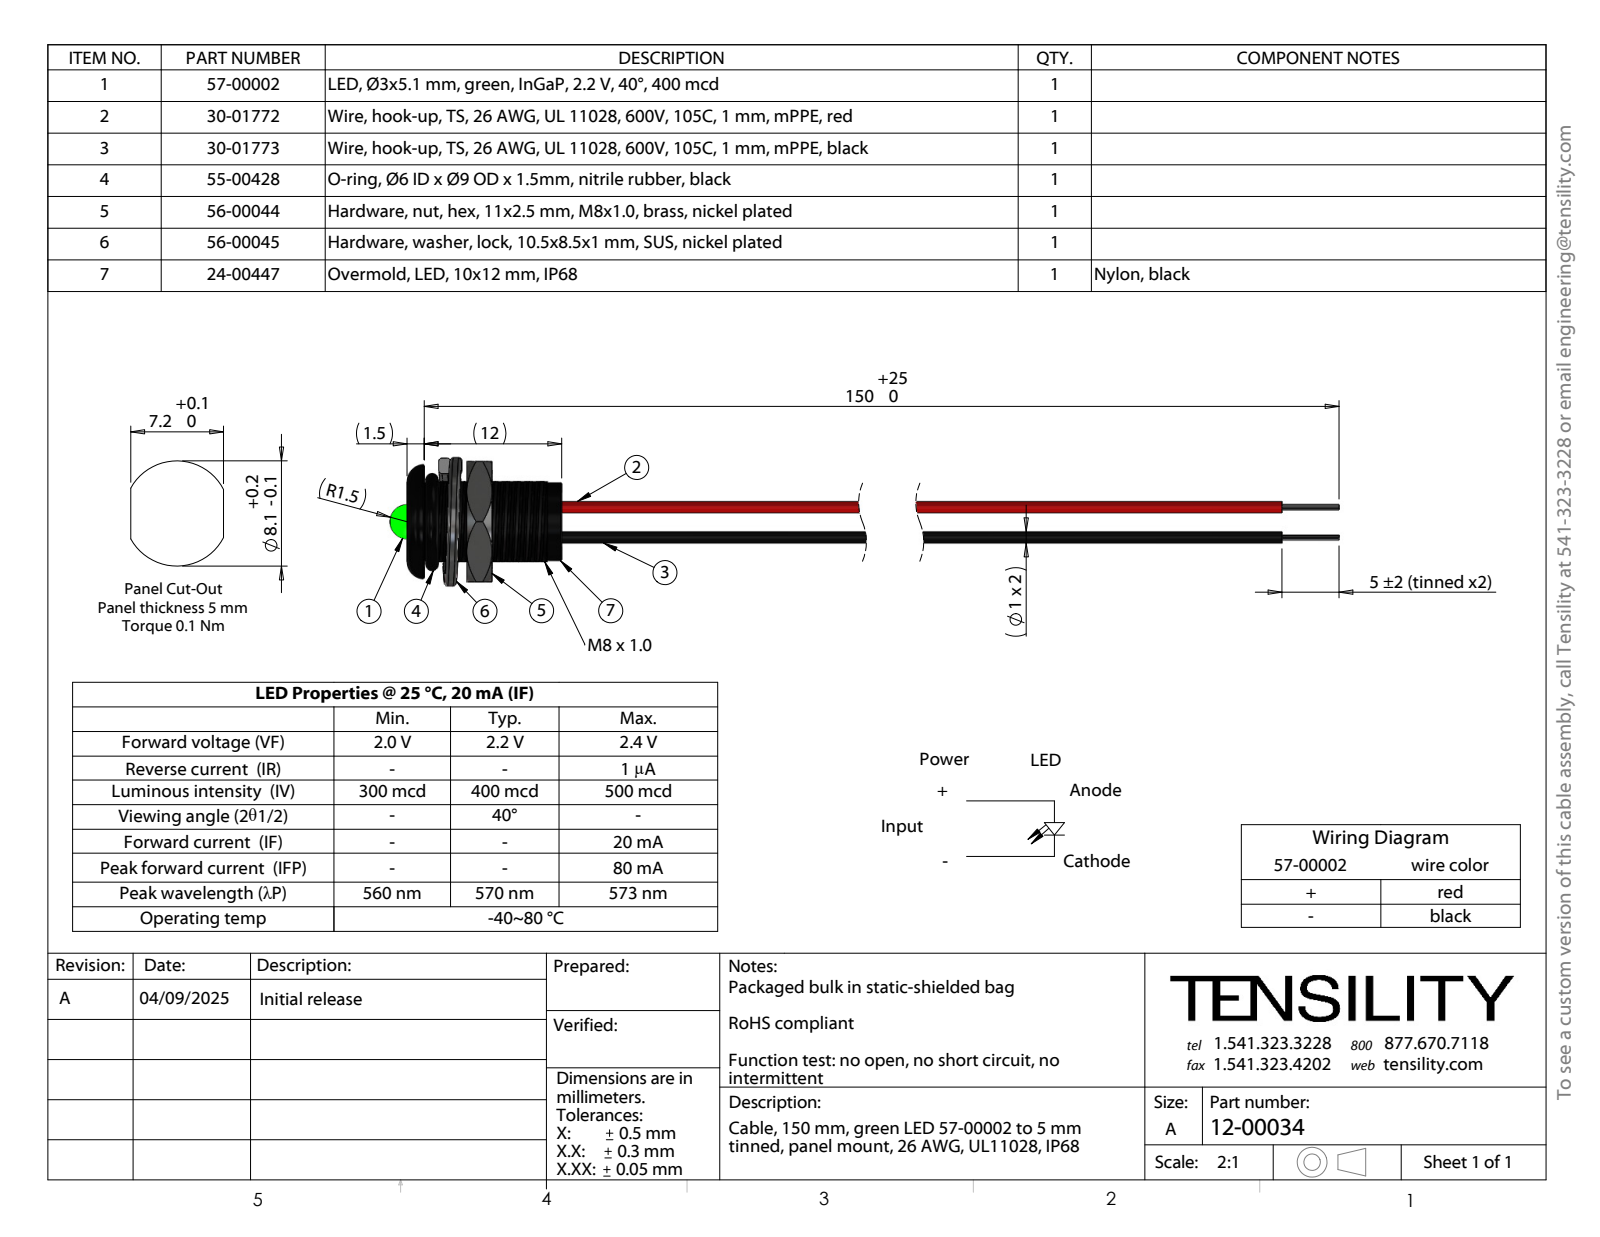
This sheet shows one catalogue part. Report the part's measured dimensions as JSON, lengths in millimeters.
{"part_name": "30-01772_stripped and tinned; 30-01773_stripped and tinned; 24-00447; 12-00034 (+4 more)", "step_written_by": "SolidWorks 2021 (CONFIG_CONTROL_DESIGN)", "units": "millimeters", "bodies": {"solids": 57, "faces": 555, "planar": 186, "cylindrical": 246, "other": 123}, "overall_size": [169.99, 12.12, 11.21], "volume_mm3": 1005, "surface_area_mm2": 5908, "round_holes": [[1, 2]], "round_bosses_or_shafts": [[1, 2], [0.5, 2], [6.8, 1], [3, 1]], "partial_cylinders_radius": [[3.48, 1], [4, 1]], "face_to_face_distances": [1.5, 13.5, 12, 10.5, 5.21, 3.71, 8.29, 7.41, 5.91, 2.2], "hole_center_spacings": [0.36, 0.38, 0.33, 2.48, 2.52, 2.43, 2.44, 2.56]}
